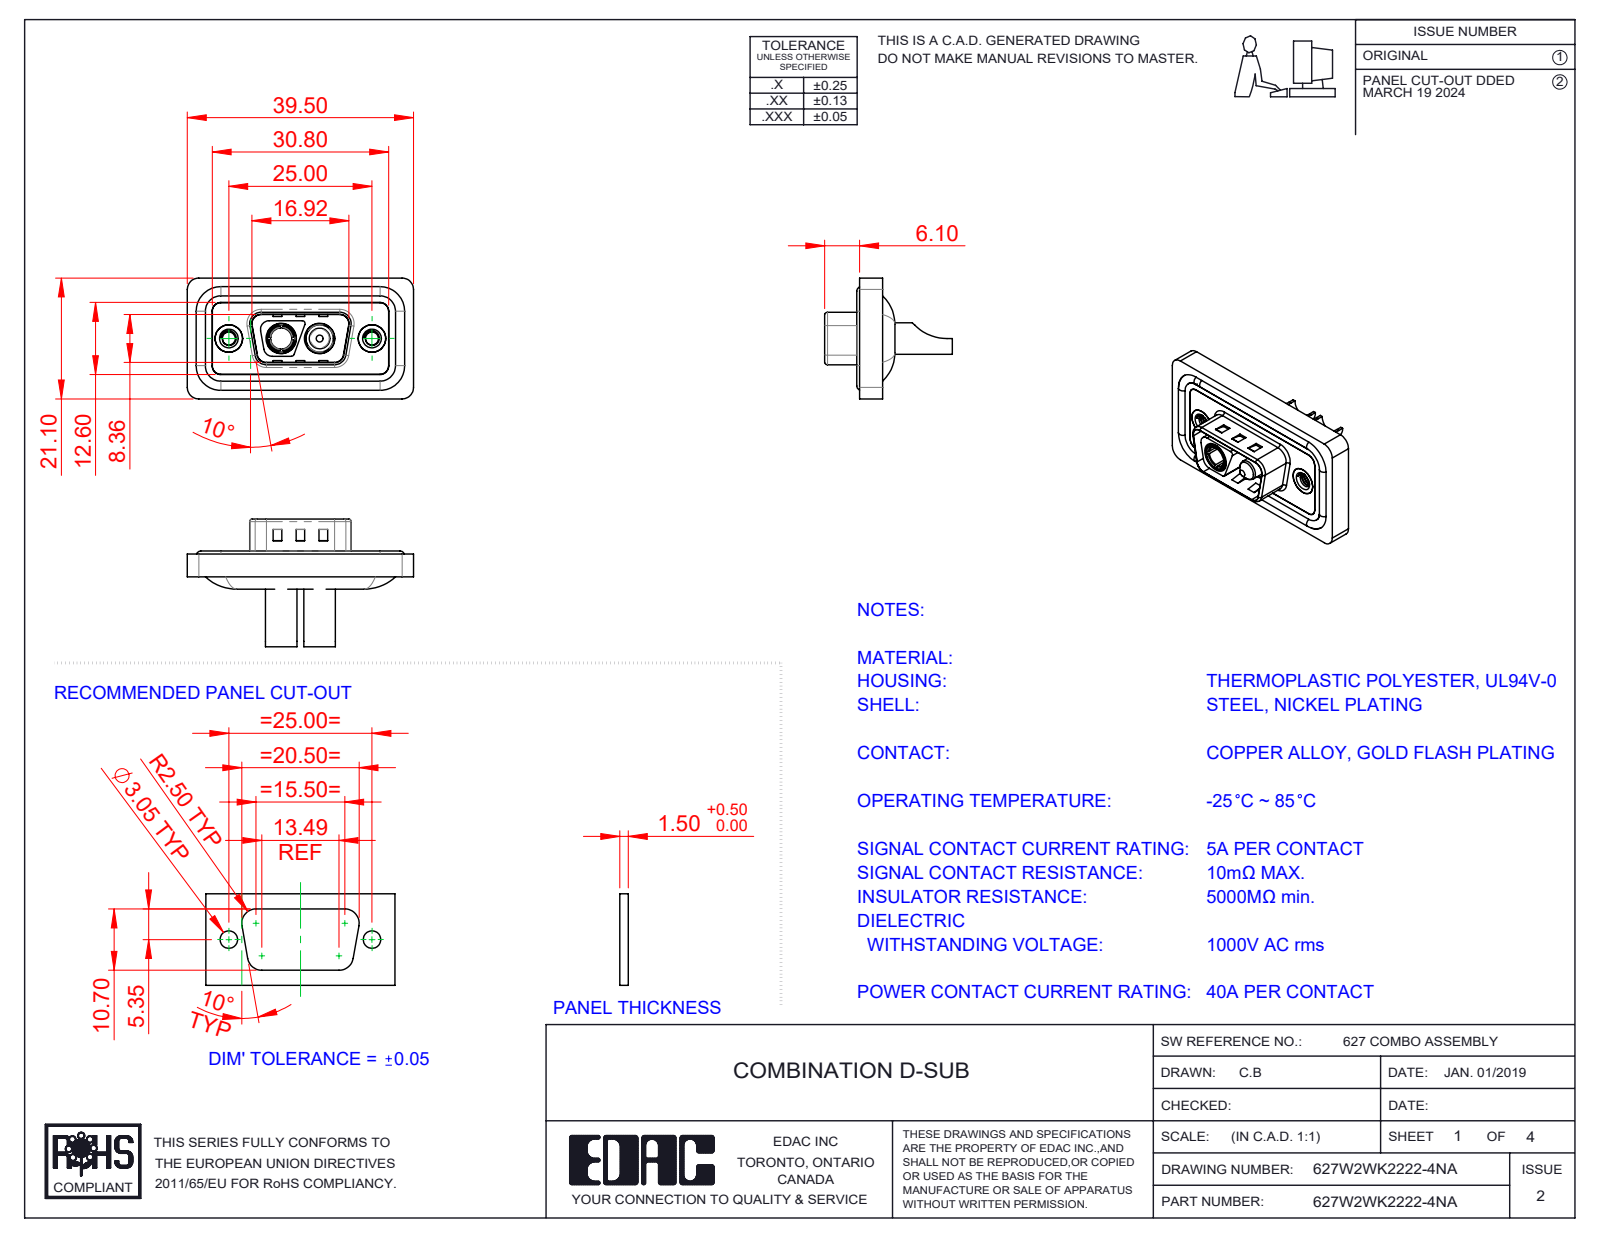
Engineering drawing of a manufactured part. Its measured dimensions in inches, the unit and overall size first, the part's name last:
Units: inches
Overall size (bounding box): 1.555 × 0.878 × 0.831
Round holes (diameter × count): ⌀0.089 ×2, ⌀0.157 ×2, ⌀0.181 ×2, ⌀0.189 ×2, ⌀0.191 ×2, ⌀0.197 ×2, ⌀0.209 ×2, ⌀0.146 ×1
Round bosses / shafts (diameter × count): ⌀0.063 ×4, ⌀0.217 ×2, ⌀0.205 ×2, ⌀0.193 ×2, ⌀0.187 ×2, ⌀0.148 ×2, ⌀0.195 ×1, ⌀0.142 ×1
Partial cylindrical surfaces — rounded edges, fillets, slot ends (radius × count): R0.059 ×24, R0.079 ×18, R0.02 ×10, R0.063 ×8, R0.01 ×4, R0.024 ×4, R0.026 ×4, R0.035 ×4
Main face-to-face distances: 0.016, 0.043, 0.114, 0.02, 0.122, 0.063, 0.098, 0.071, 0.126, 0.059
Hole centre spacings: 0.36, 0.624, 0.265, 0.984
Volume: 0.283 in³ · Surface area: 11.81 in²
Bodies: 11 solids, 540 faces (193 planar, 231 cylindrical, 116 other)
Part name (STEP PRODUCT): Power Pin_40A SC; 627Combo Housing_2WK2; 627Combo Threaded Rivet_A; 627Combo Shell Rear_09 Contacts (+4 more)
STEP written by: SolidWorks 2023 (CONFIG_CONTROL_DESIGN)
